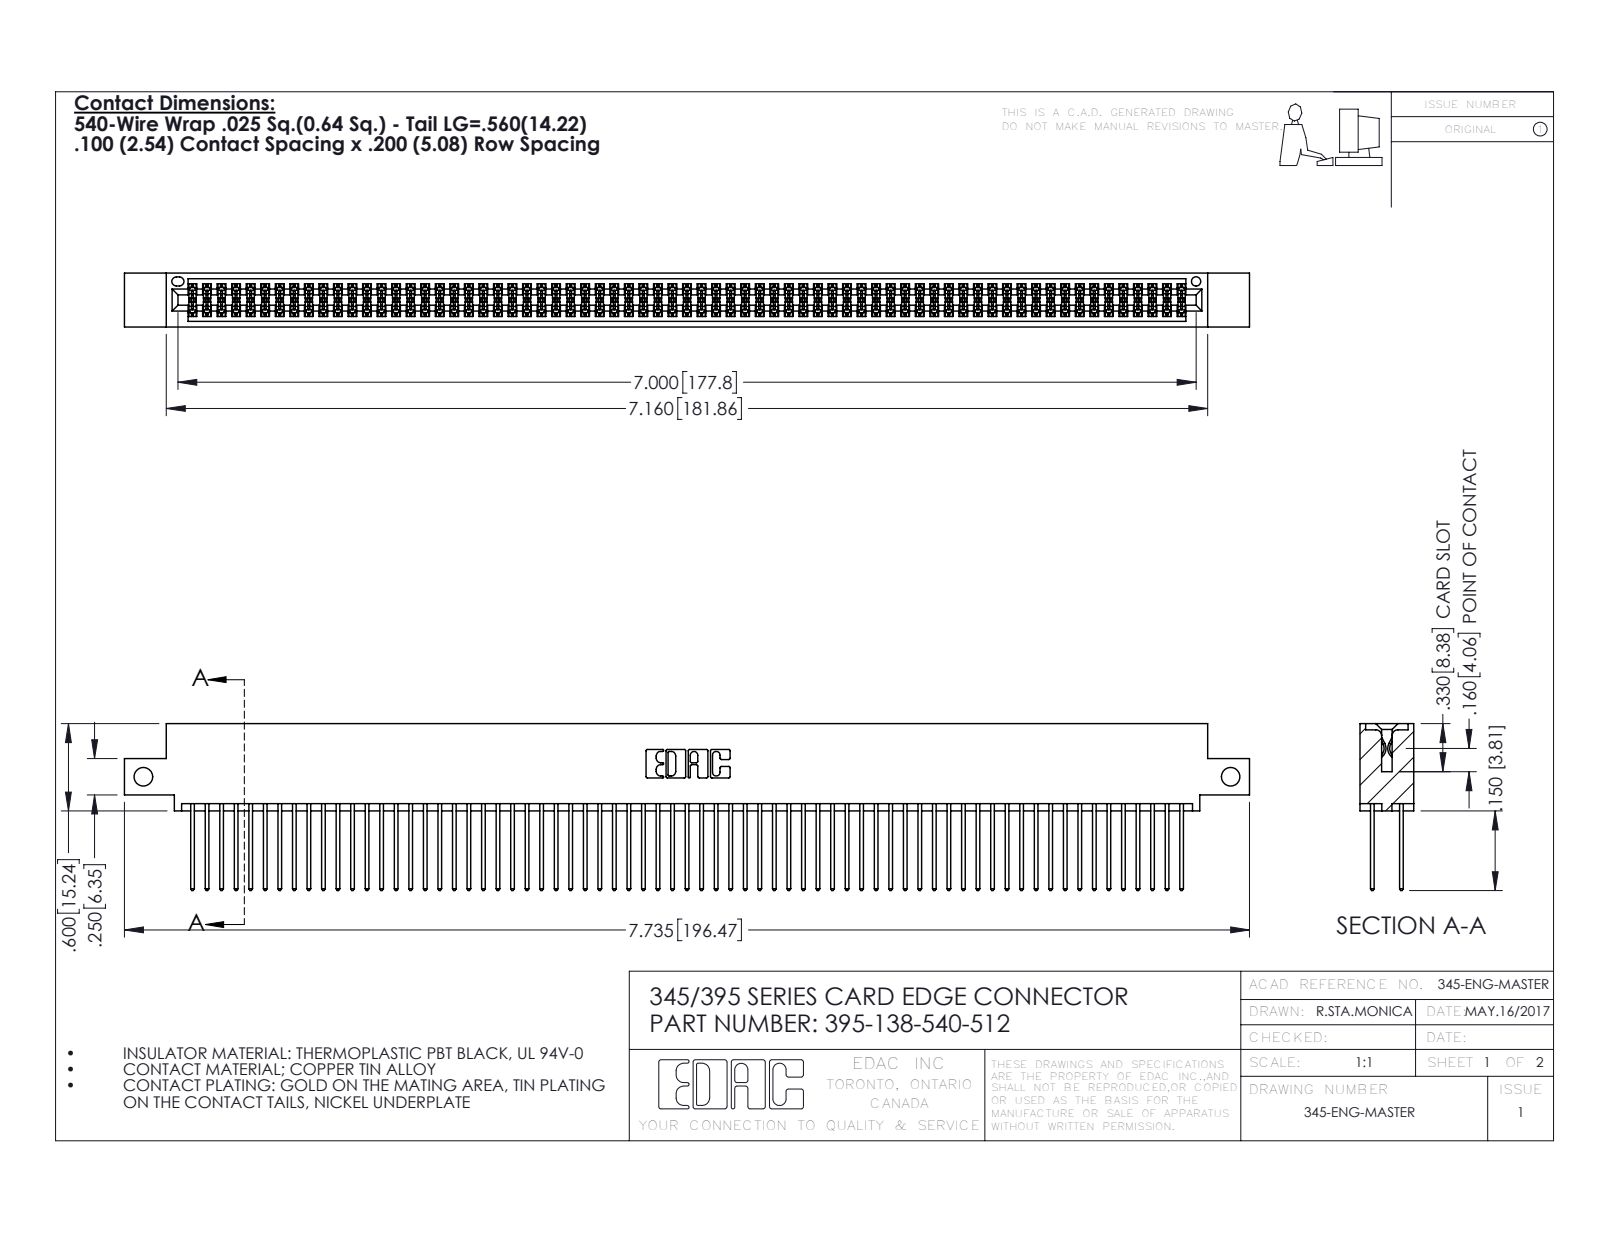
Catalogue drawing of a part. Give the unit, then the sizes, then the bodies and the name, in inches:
Units: inches
Overall size (bounding box): 7.735 × 1.147 × 0.37
Round holes (diameter × count): ⌀0.128 ×2, ⌀0.064 ×1
Partial cylindrical surfaces — rounded edges, fillets, slot ends (radius × count): R0.006 ×207, R0.01 ×138, R0.01 ×22, R0.007 ×6, R0.031 ×6, R0.026 ×3, R0.014 ×2, R0.019 ×2
Main face-to-face distances: 0.072, 0.298, 0.2, 0.098, 0.272, 0.025, 0.225, 0.37, 0.175, 0.149
Hole centre spacings: 7.475
Volume: 1.202 in³ · Surface area: 49.64 in²
Bodies: 139 solids, 7030 faces (4638 planar, 2392 cylindrical, 0 other)
Part name (STEP PRODUCT): 395-138-540-512; 345-292-001_345-293-140; 345 Part_0.110 Offset - Side Mount
STEP written by: SolidWorks 2016 (CONFIG_CONTROL_DESIGN)
